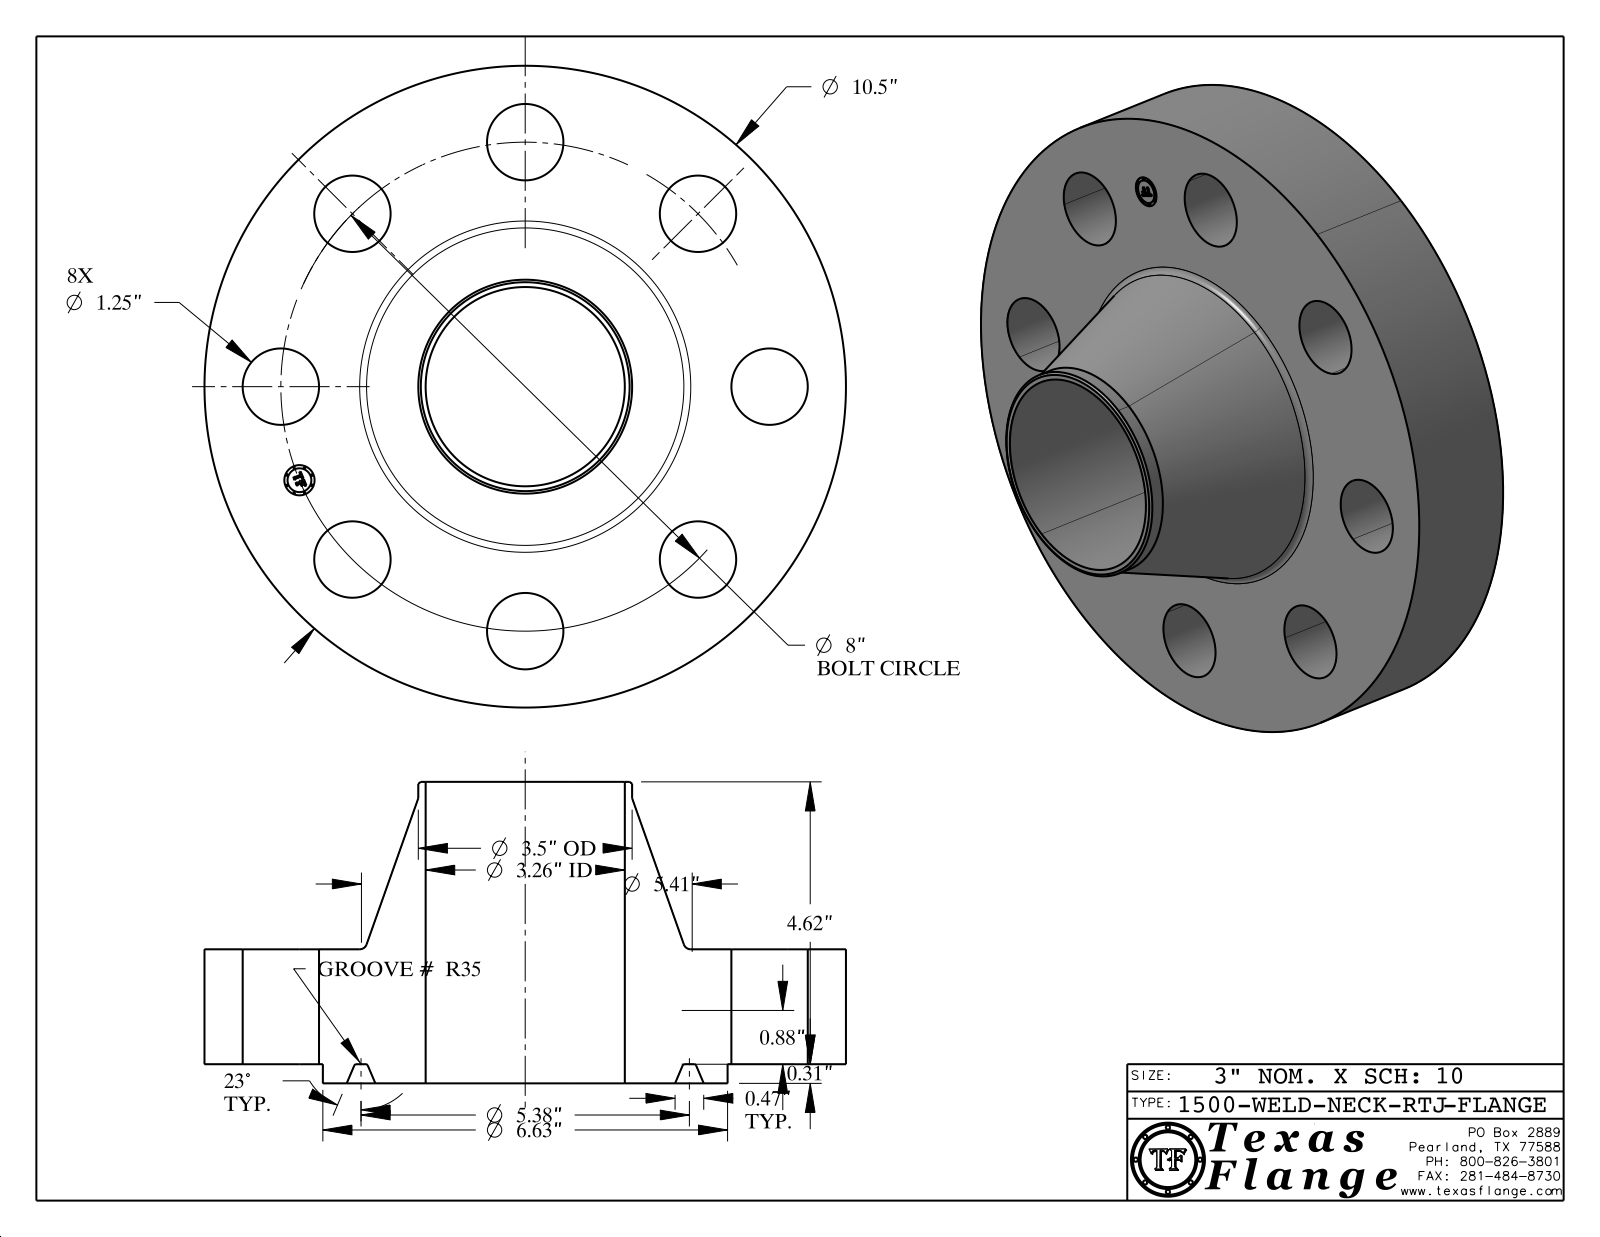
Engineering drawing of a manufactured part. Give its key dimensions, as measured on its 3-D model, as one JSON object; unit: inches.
{"part_name": "1500-WELD-NECK-RTJ", "step_written_by": "CATIA V5 STEP AP214 (AUTOMOTIVE_DESIGN)", "units": "inches", "bodies": {"solids": 1, "faces": 429, "planar": 371, "cylindrical": 44, "other": 14}, "overall_size": [10.5, 10.5, 4.933], "volume_in3": 152.4, "surface_area_in2": 348.3, "round_holes": [[1.25, 8], [0.495, 1], [3.26, 1]], "round_bosses_or_shafts": [[0.03, 8], [10.5, 1], [6.625, 1], [3.5, 1], [0.39, 1]], "face_to_face_distances": [1.88, 0.313, 2.193, 4.933, 4.62, 2.74, 0.015, 2.178, 1.865, 2.755], "hole_center_spacings": [4, 3.061, 5.657, 7.391, 1.561, 6.652, 7.846, 8]}
